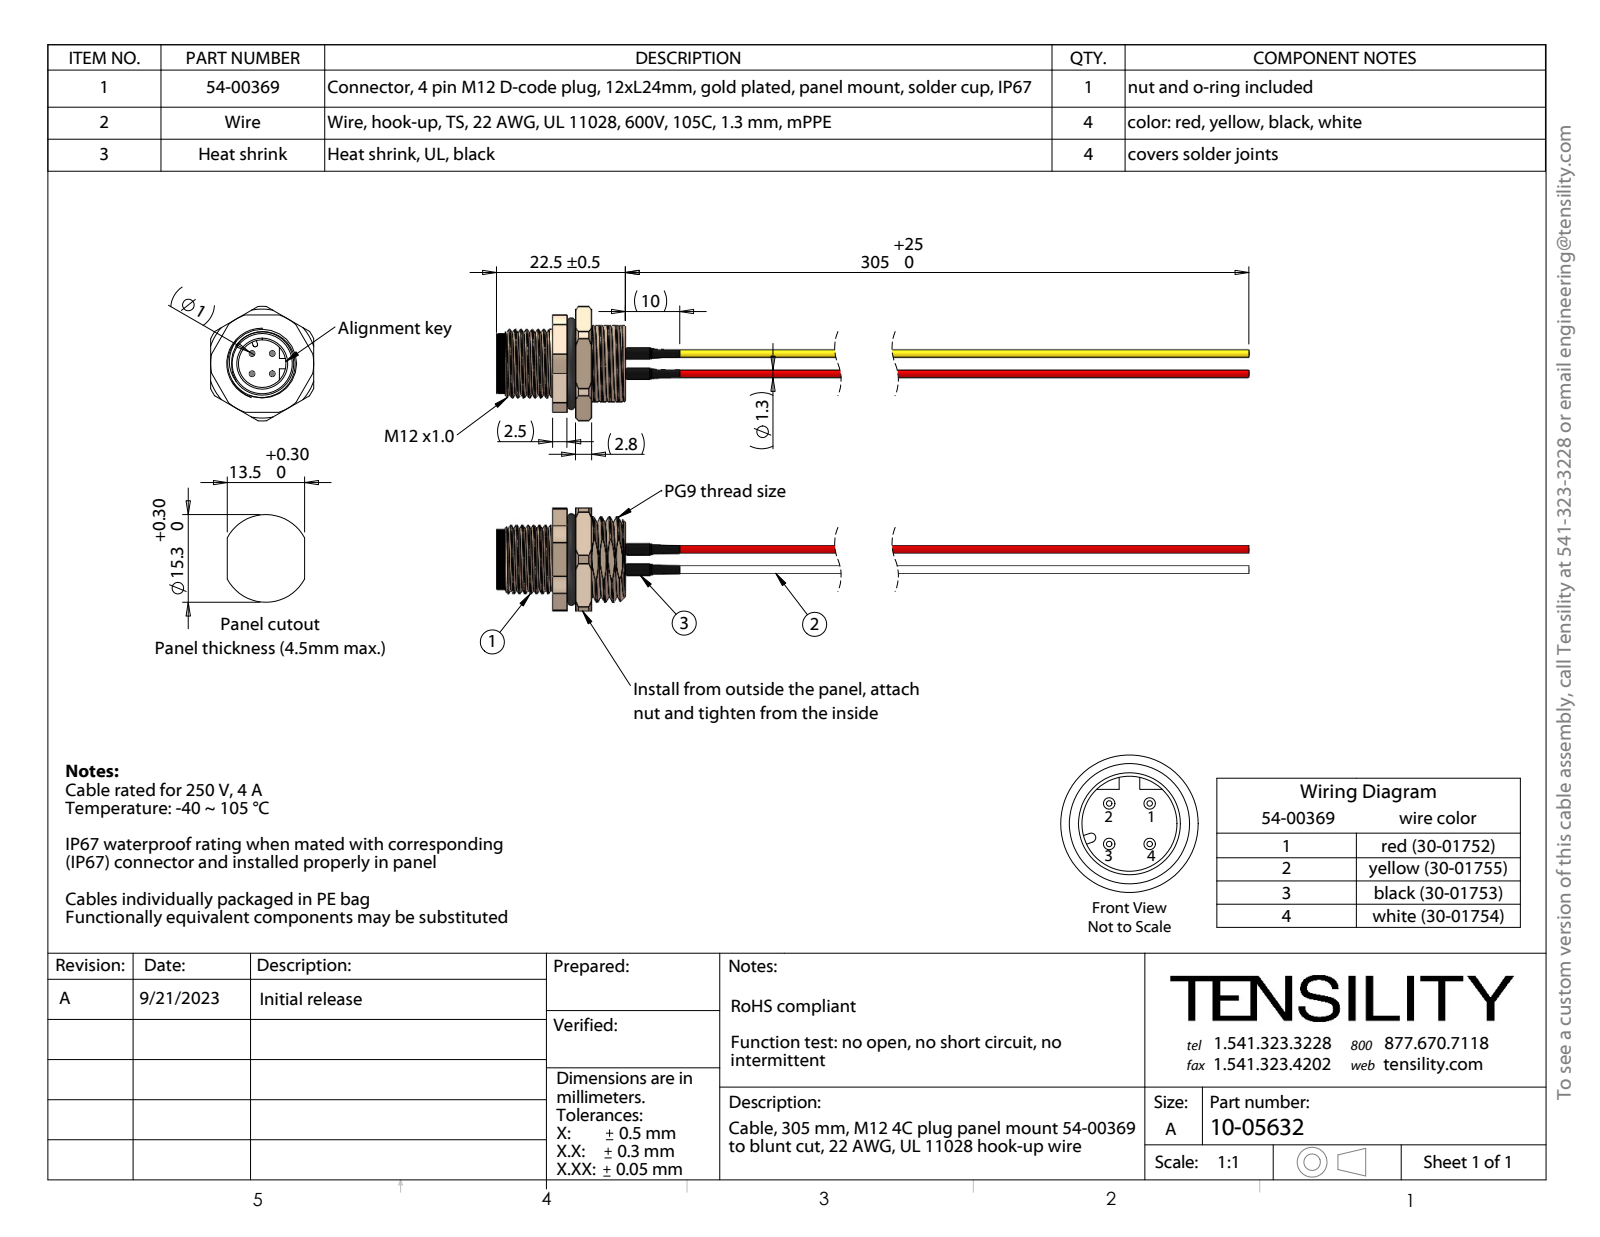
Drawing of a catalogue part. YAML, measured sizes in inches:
part_name: "10-05632_revA; 54-00369-01; 54-00369; 30-01753_blunt cut (+8 more)"
step_written_by: "SolidWorks 2021 (CONFIG_CONTROL_DESIGN)"
units: inches
bodies: {solids: 84, faces: 787, planar: 238, cylindrical: 432, other: 117}
overall_size: [6.85, 0.787, 0.709]
volume: 0.237
surface_area: 28.21
round_holes:
  - {diameter: 0.031, count: 4}
  - {diameter: 0.039, count: 4}
  - {diameter: 0.315, count: 1}
  - {diameter: 0.327, count: 1}
  - {diameter: 0.366, count: 1}
  - {diameter: 0.433, count: 1}
  - {diameter: 0.551, count: 1}
round_bosses_or_shafts:
  - {diameter: 0.079, count: 4}
  - {diameter: 0.055, count: 4}
  - {diameter: 0.051, count: 4}
  - {diameter: 0.512, count: 1}
  - {diameter: 0.472, count: 1}
  - {diameter: 0.413, count: 1}
  - {diameter: 0.354, count: 1}
partial_cylinders:
  - {radius: 0.077, count: 2}
  - {radius: 0.016, count: 1}
  - {radius: 0.295, count: 1}
  - {radius: 0.354, count: 1}
  - {radius: 0.394, count: 1}
face_to_face_distances: [0.256, 0.059, 0.48, 0.157, 0.098, 0.323, 0.126, 0.382, 0.067, 0.224]
hole_center_spacings: [0.013, 0.019, 0.013, 0.015, 0.018, 0.015, 0.205, 0.021]
